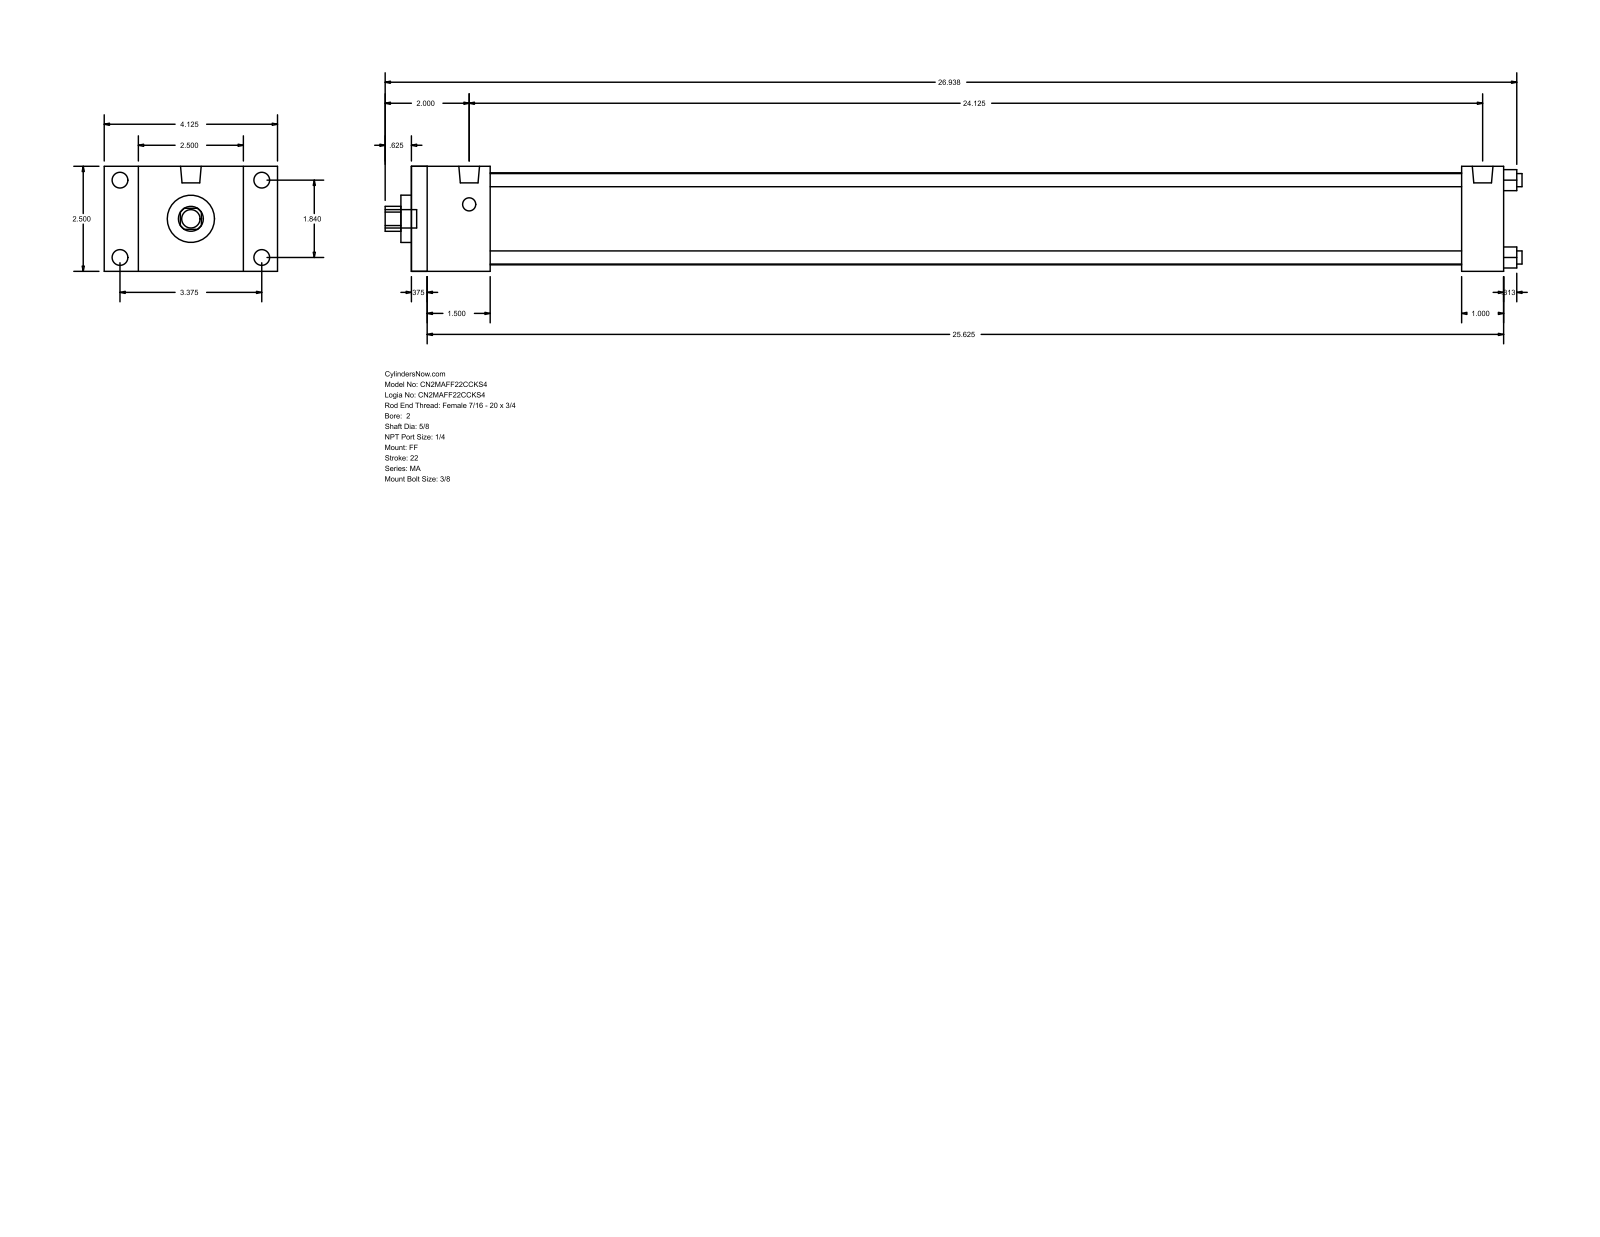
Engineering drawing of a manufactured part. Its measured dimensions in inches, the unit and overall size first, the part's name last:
Units: inches
Overall size (bounding box): 27.063 × 4.125 × 2.5
Round holes (diameter × count): ⌀0.313 ×4, ⌀0.625 ×1, ⌀1.125 ×1, ⌀2.19 ×1
Round bosses / shafts (diameter × count): ⌀0.375 ×4, ⌀0.313 ×4, ⌀0.492 ×2, ⌀0.437 ×1
Partial cylindrical surfaces — rounded edges, fillets, slot ends (radius × count): R0.297 ×1
Main face-to-face distances: 2.5, 26, 0.375, 25.625, 1.5, 1.875, 25, 24.625, 23.125, 24.125
Hole centre spacings: 1.301, 1.84, 2.602
Bodies: 0 solids, 92 faces (64 planar, 28 cylindrical, 0 other)
Part name (STEP PRODUCT): MA_FF__0200_0.625
STEP written by: GSSL Pune (CONFIG_CONTROL_DESIGN)
